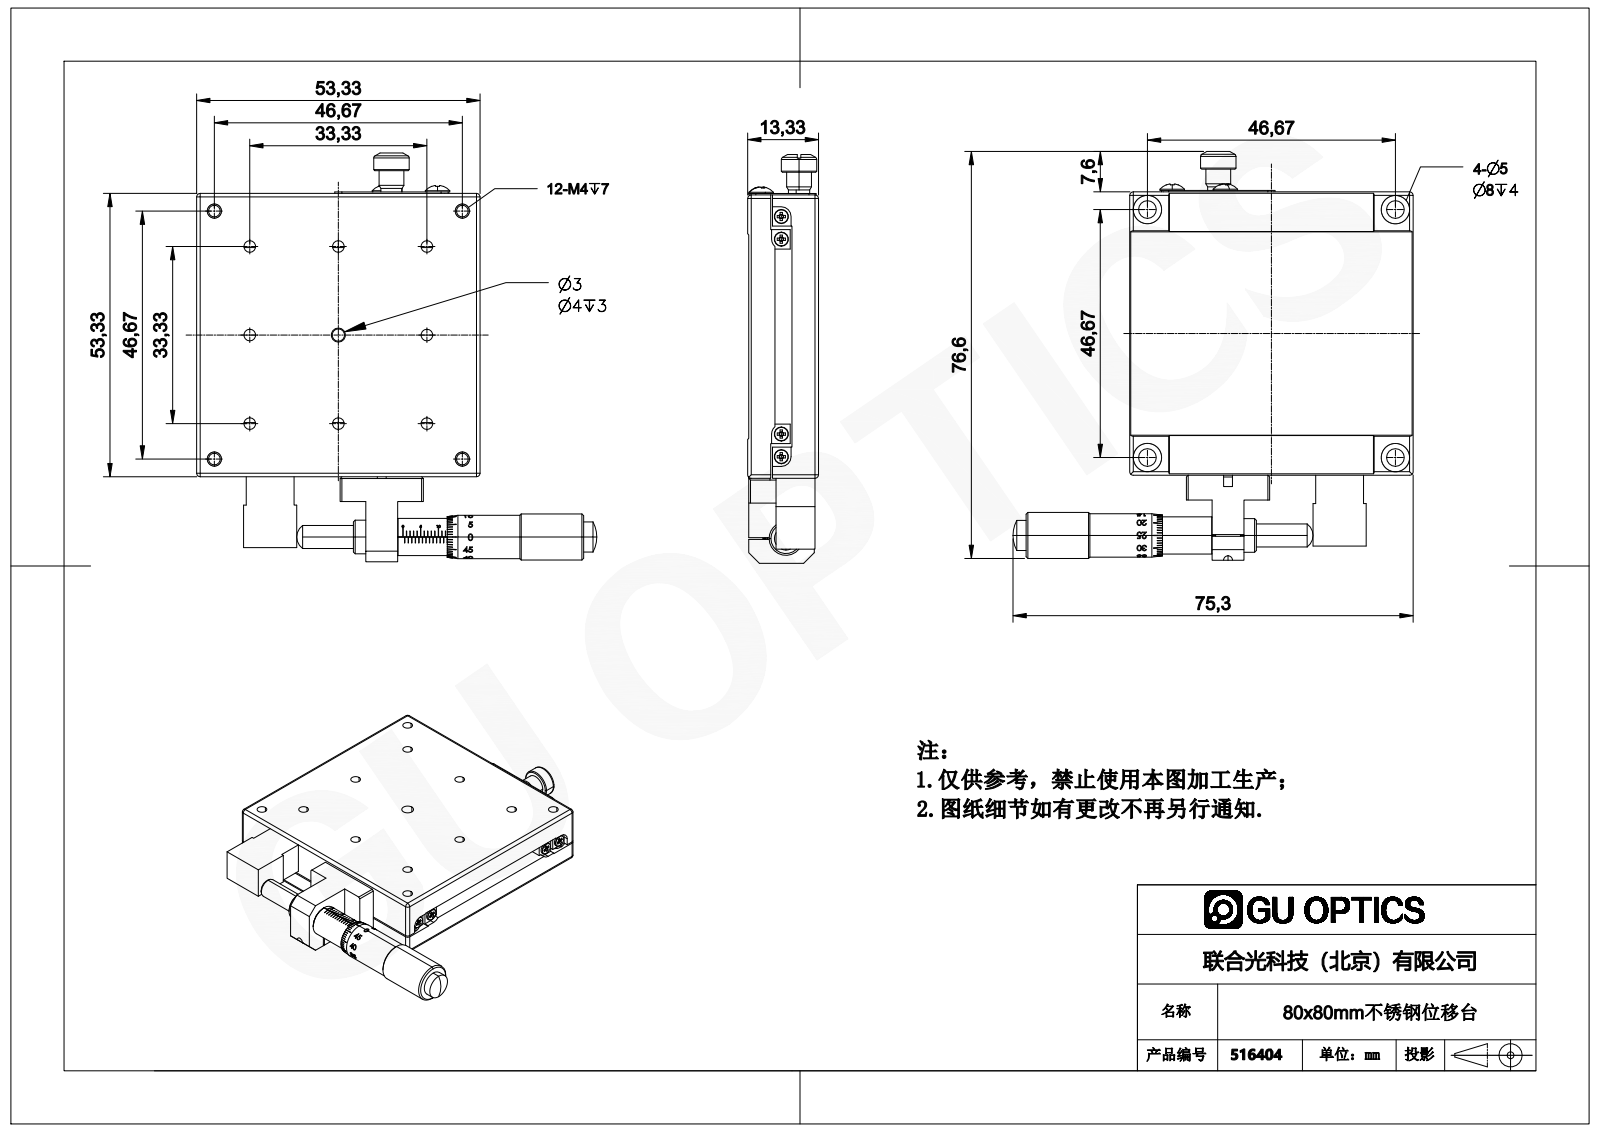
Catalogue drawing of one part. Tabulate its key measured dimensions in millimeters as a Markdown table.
| quantity | value |
| --- | --- |
| part name | MX80-SS |
| STEP written by | SolidWorks 2020 (CONFIG_CONTROL_DESIGN) |
| units | millimeters |
| bodies | 2 solids, 791 faces (412 planar, 243 cylindrical, 136 other) |
| overall size | 115.4 × 112.95 × 20 |
| volume | 118 333 mm³ |
| surface area | 44 571 mm² |
| round holes (diameter × count) | 3.3 × 12, 5 × 4, 8 × 4, 6 × 2, 2.5 × 1, 3.4 × 1, 3.5 × 1, 4 × 1, 6.5 × 1, 9.5 × 1, 10.7 × 1 |
| round bosses / shafts (diameter × count) | 4 × 4, 6.9 × 2, 5.5 × 2, 13 × 1, 12.25 × 1, 10.5 × 1, 10 × 1, 9.1 × 1 |
| partial cylindrical surfaces (radius × count) | 1 × 12, 2 × 4, 2.75 × 4, 1.65 × 2 |
| main face-to-face distances | 7.5, 12.3, 12.2, 19.7, 4.8, 7.4, 5.5, 0.5, 80, 13 |
| hole center spacings | 25, 35.36, 36.4, 55.9, 60.83, 69.46, 50, 14.14 |
